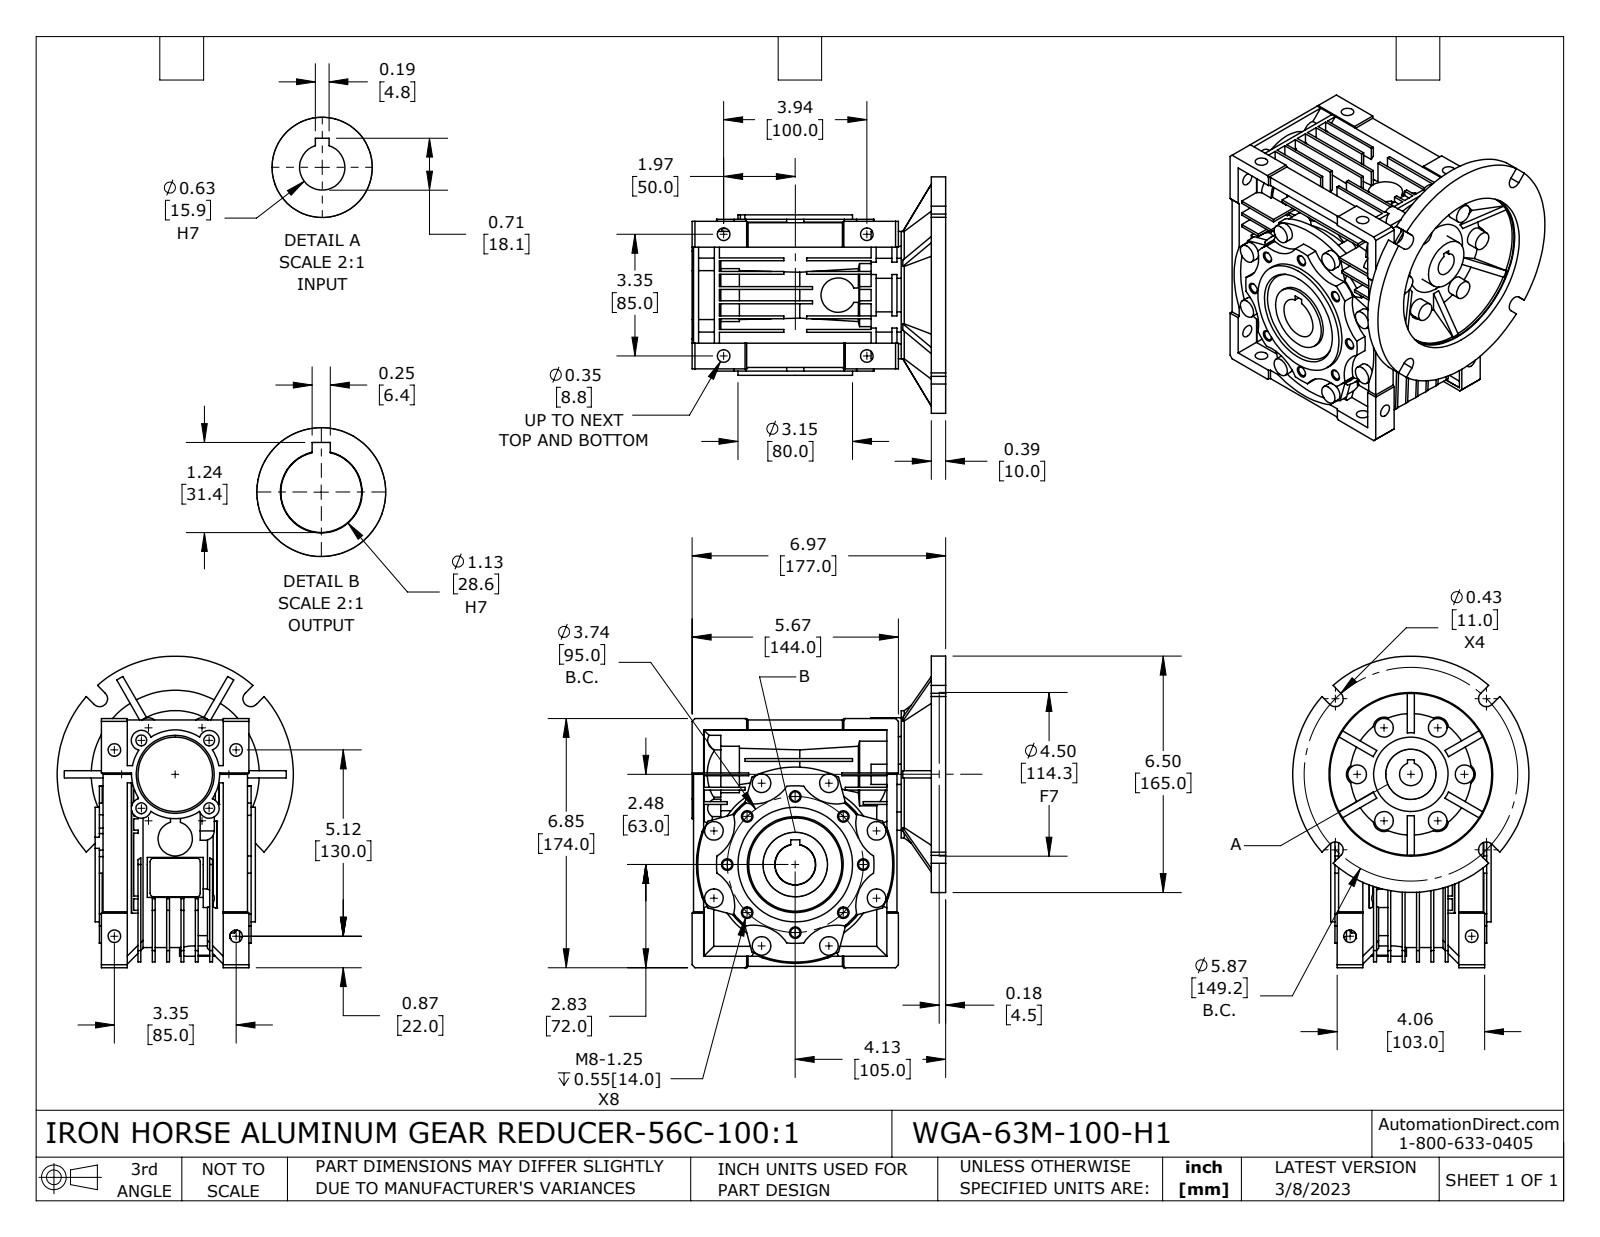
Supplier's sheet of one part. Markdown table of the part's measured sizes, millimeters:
| quantity | value |
| --- | --- |
| part name | WGA-63M-100-H1 |
| STEP written by | SolidWorks 2021 (CONFIG_CONTROL_DESIGN) |
| units | millimeters |
| bodies | 4 solids, 1231 faces (759 planar, 331 cylindrical, 141 other) |
| overall size | 217.5 × 177 × 165 |
| volume | 1 917 000 mm³ |
| surface area | 366 500 mm² |
| round holes (diameter × count) | 6.7 × 8, 6.7 × 8, 8.8 × 8, 7.6 × 4, 15.9 × 1, 16.5 × 1, 28.6 × 1, 34 × 1, 37 × 1, 45 × 1, 52 × 1, 113 × 1 |
| round bosses / shafts (diameter × count) | 13 × 14, 24 × 3, 165 × 1, 110 × 1, 89 × 1, 80 × 1, 69 × 1, 62 × 1 |
| partial cylindrical surfaces (radius × count) | 7 × 10, 27 × 8, 7.5 × 6, 2.5 × 4, 5.5 × 4, 8.4 × 1, 29.5 × 1, 30.5 × 1 |
| main face-to-face distances | 10, 8, 20, 2, 30, 7, 12, 18, 40, 31 |
| hole center spacings | 36.3, 47.5, 67.2, 87.8, 33.5, 47.4, 85, 20 |
